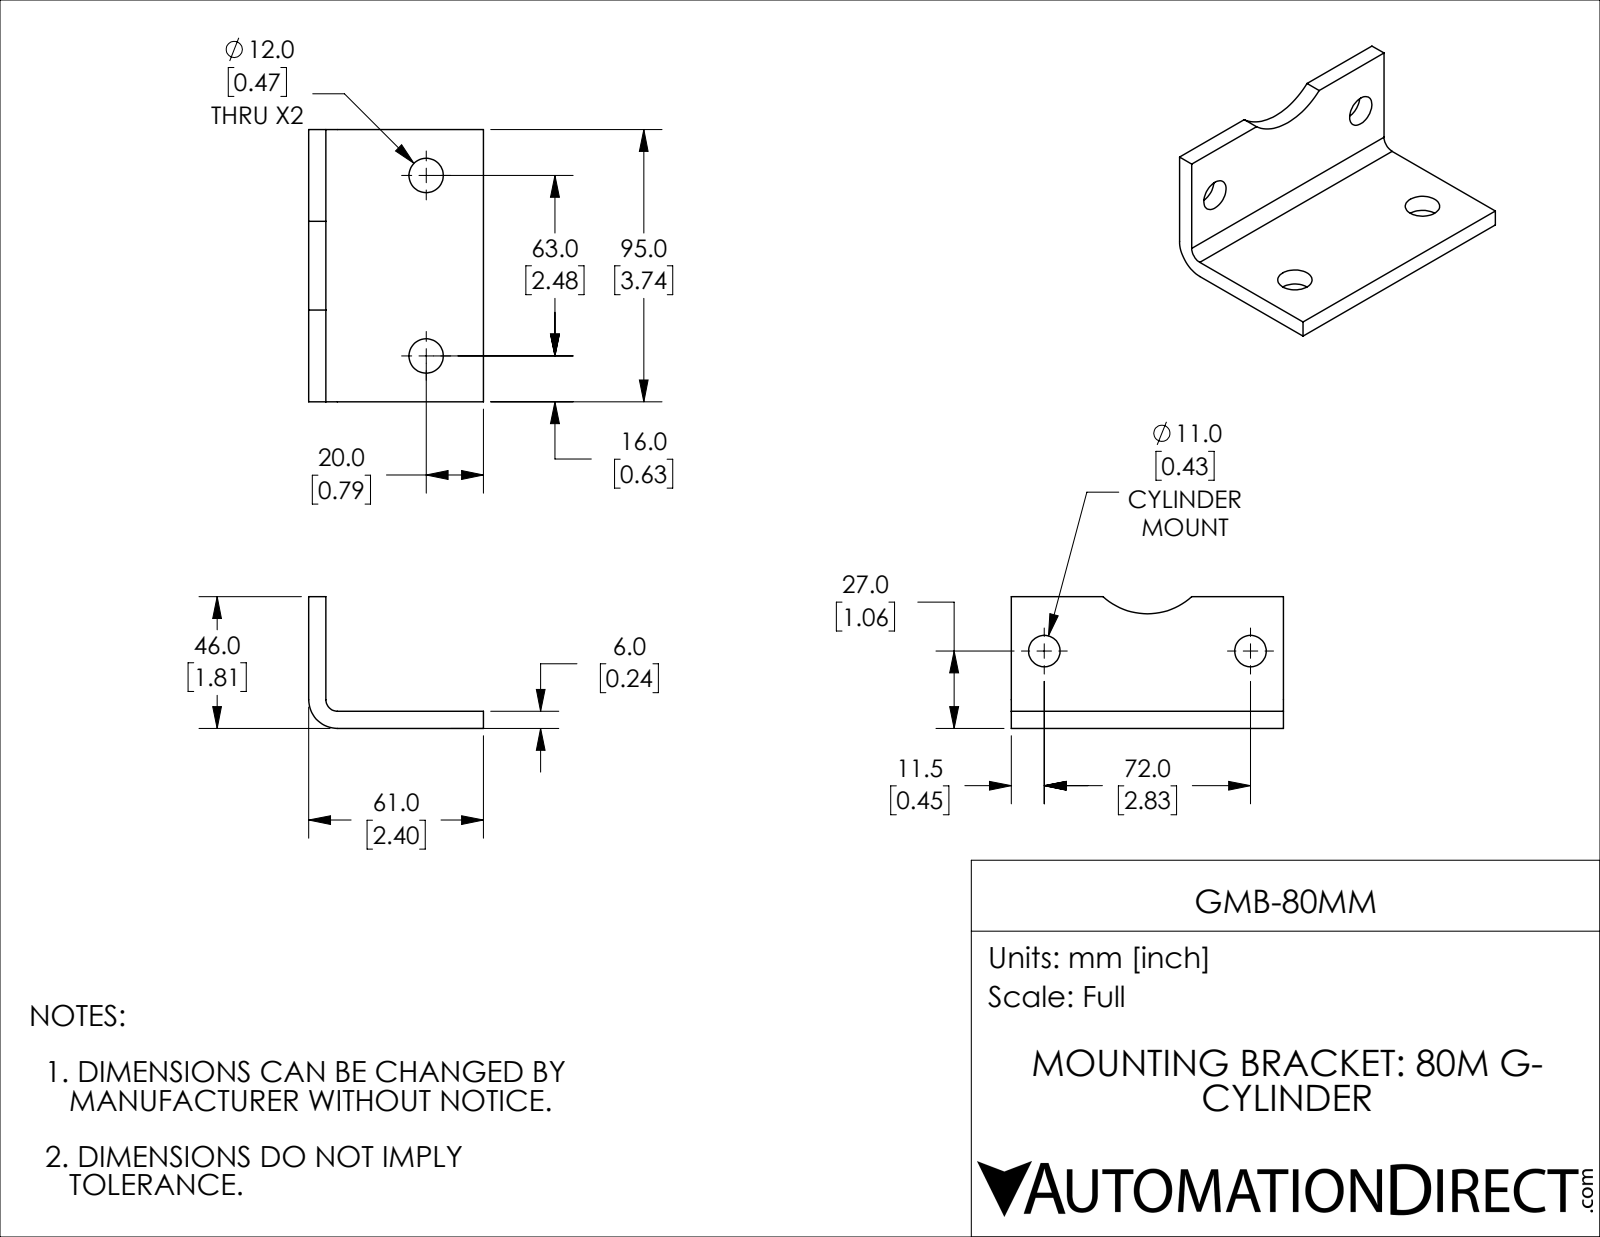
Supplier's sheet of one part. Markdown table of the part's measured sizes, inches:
| quantity | value |
| --- | --- |
| part name | GMB-80MM |
| STEP written by | SolidWorks 2018 (AUTOMOTIVE_DESIGN) |
| units | inches |
| bodies | 1 solid, 20 faces (9 planar, 11 cylindrical, 0 other) |
| overall size | 3.74 × 2.402 × 1.811 |
| volume | 3.209 in³ |
| surface area | 32.14 in² |
| round holes (diameter × count) | 0.433 × 2, 0.472 × 2 |
| partial cylindrical surfaces (radius × count) | 0.157 × 1, 0.394 × 1, 0.906 × 1 |
| main face-to-face distances | 0.236, 3.74, 2.402, 2.165, 1.811, 1.575 |
| hole center spacings | 2.48, 2.835 |
